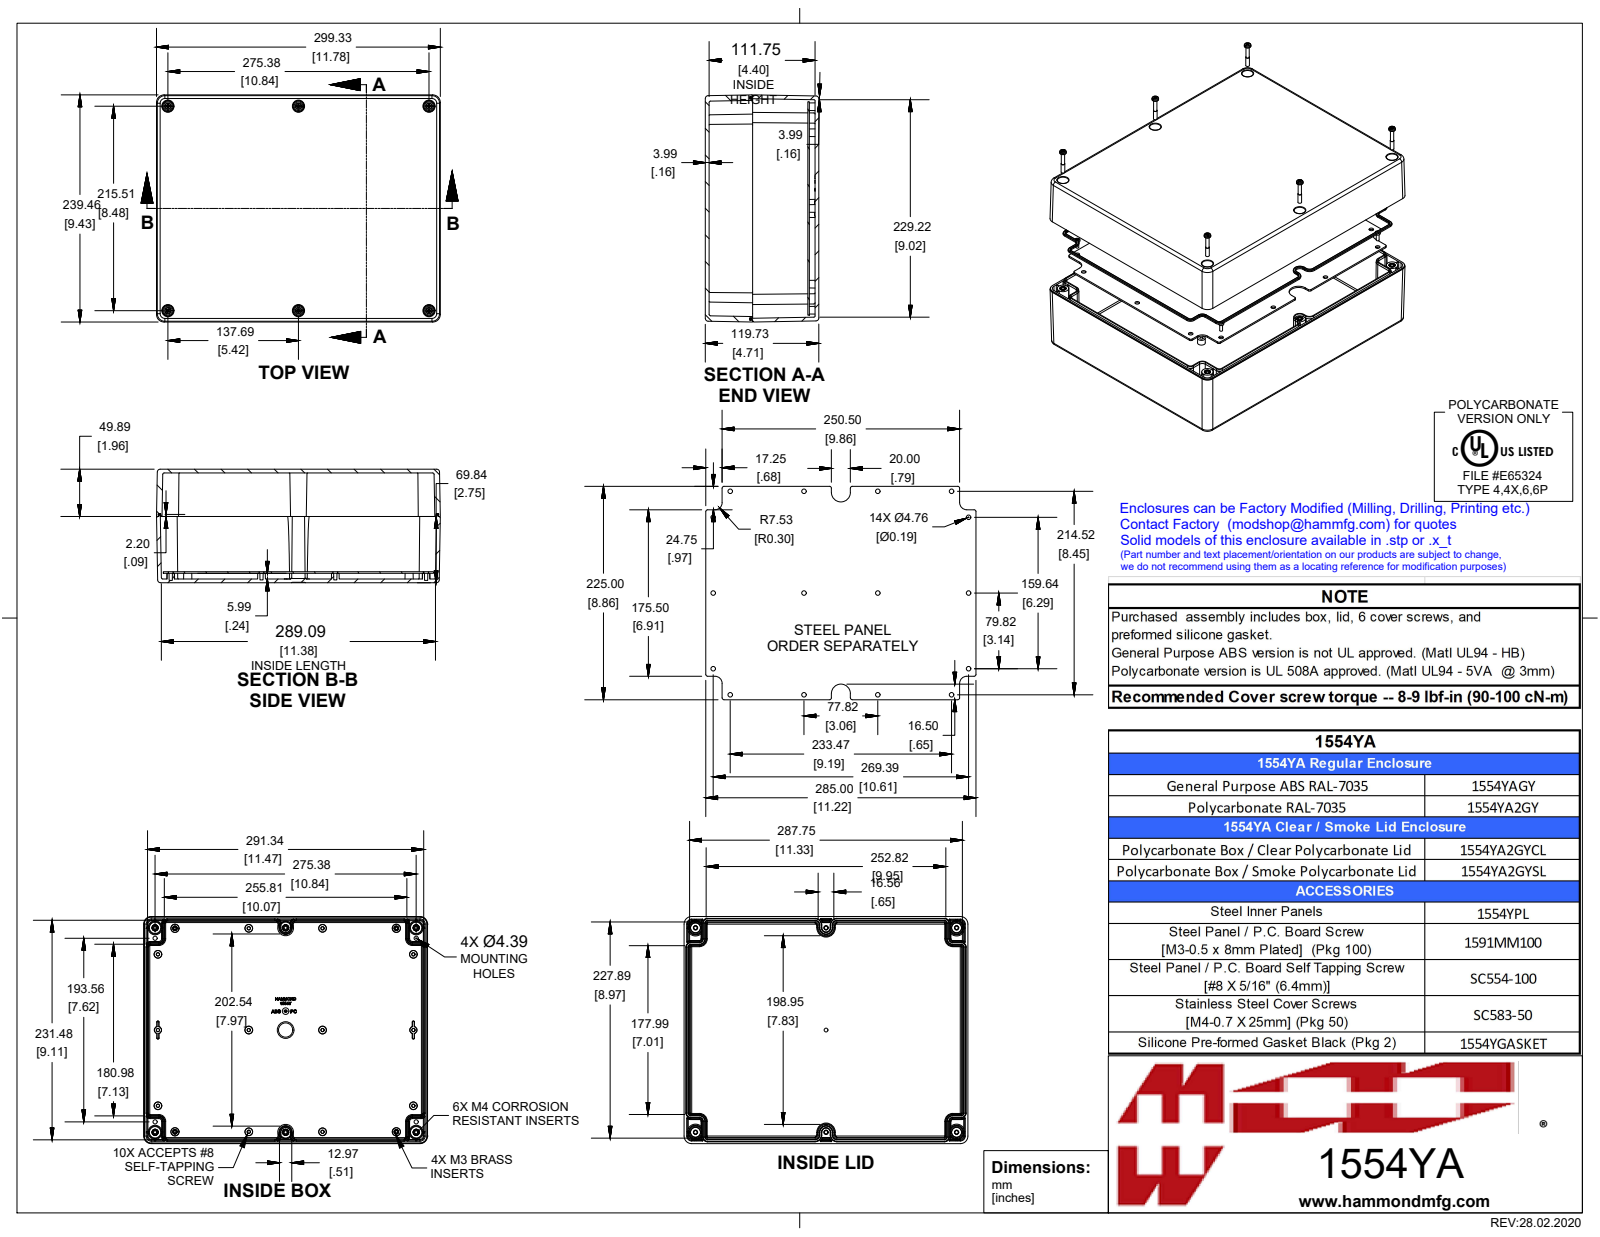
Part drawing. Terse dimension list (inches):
name: 1554YA2GY
written by: SolidWorks 2019 (AUTOMOTIVE_DESIGN)
unit: in
bodies: 24 solids, 3206 faces (904 planar, 706 cylindrical, 1596 other)
size: 11.811 × 9.449 × 4.724
volume: 79.3 in³; area: 1 174 in²
holes: 16× ⌀0.187, 6× ⌀0.128, 6× ⌀0.142, 4× ⌀0.097, 1× ⌀0.276
bosses: 6× ⌀0.272, 6× ⌀0.25, 6× ⌀0.213, 6× ⌀0.21, 6× ⌀0.152, 6× ⌀0.137, 5× ⌀0.118, 4× ⌀0.19
rounds: 30× R0.02, 20× R0.012, 14× R0.031, 12× R0.079, 12× R0.118, 8× R0.047, 8× R0.315, 6× R0.028
face distances: 0.157, 4.567, 4.724, 0.236, 0.394, 4.331, 4.409, 4.173, 0.064, 0.458
hole spacings: 5.229, 3.071, 9.004, 0.827, 1.109, 1.294, 1.535, 3.15
